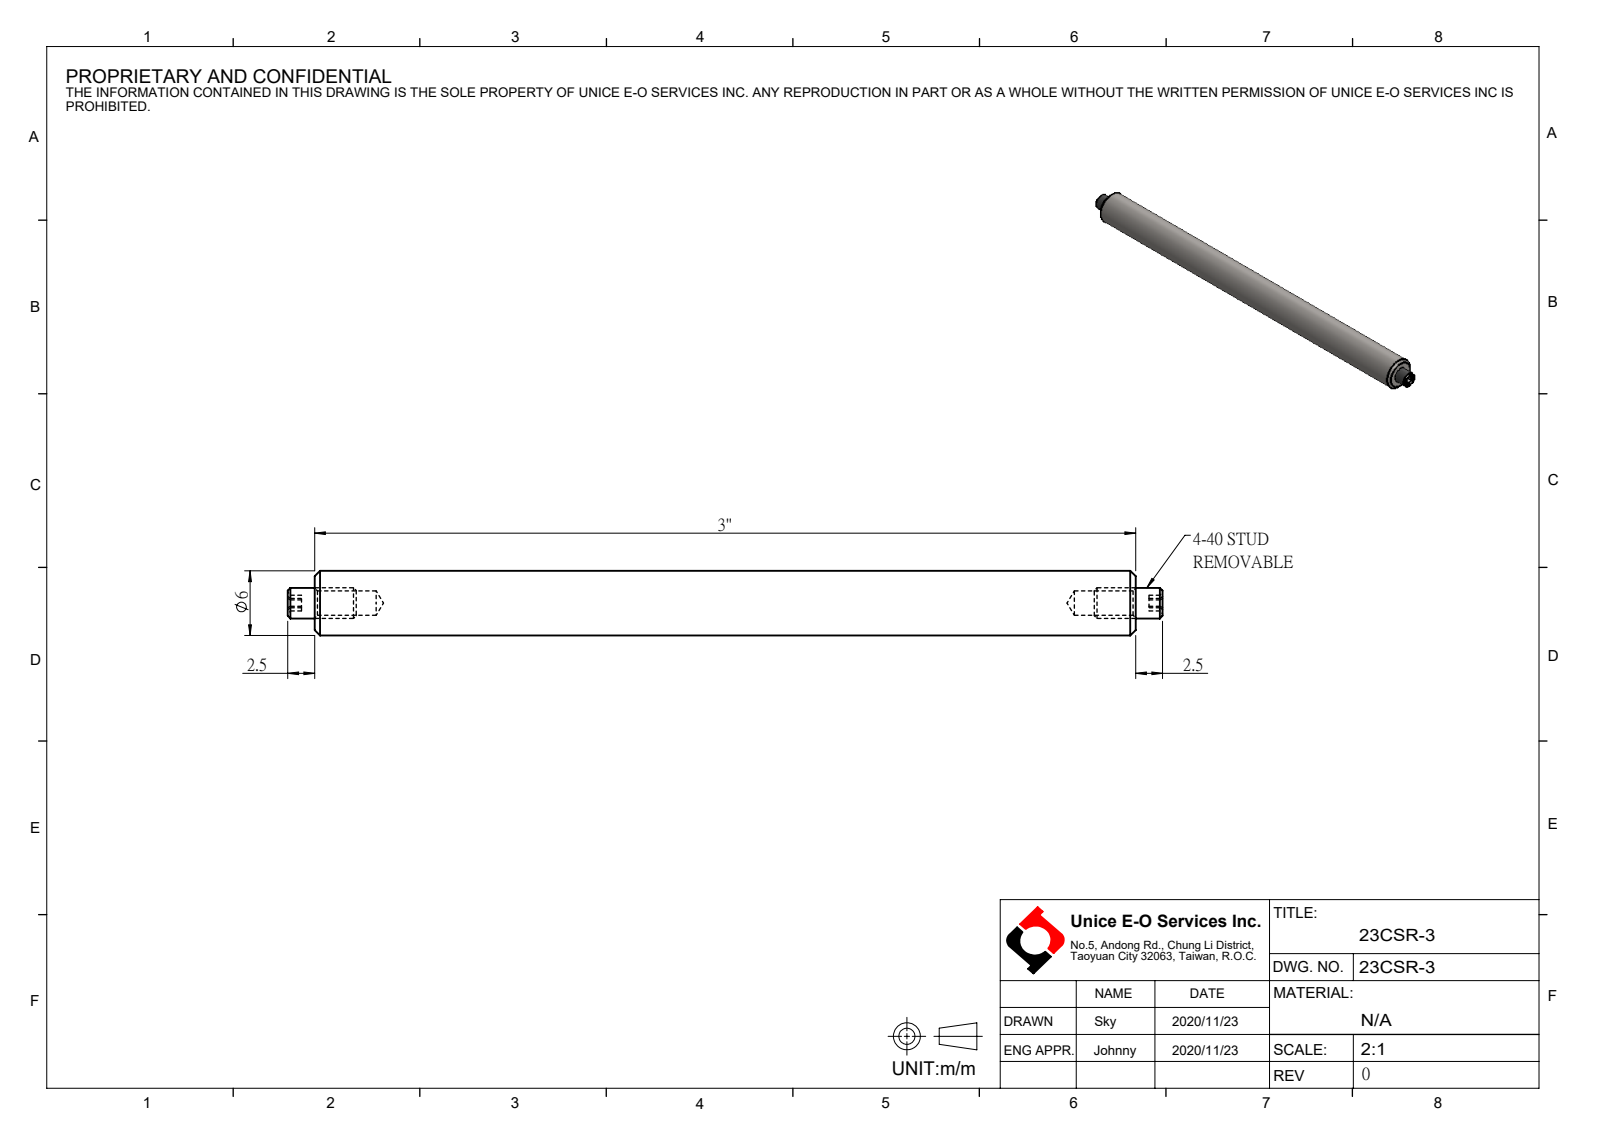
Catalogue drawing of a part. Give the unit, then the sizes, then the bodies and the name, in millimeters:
Units: millimetres
Overall size (bounding box): 81.2 × 6 × 6
Round bosses / shafts (diameter × count): ⌀6 ×1, ⌀2.84 ×1
Main face-to-face distances: 76.2, 1.27, 2.5, 78.7, 81.2
Bodies: 0 solids, 42 faces (28 planar, 6 cylindrical, 8 other)
Part name (STEP PRODUCT): 23CSR-3
STEP written by: SolidWorks 2016 (AUTOMOTIVE_DESIGN)
